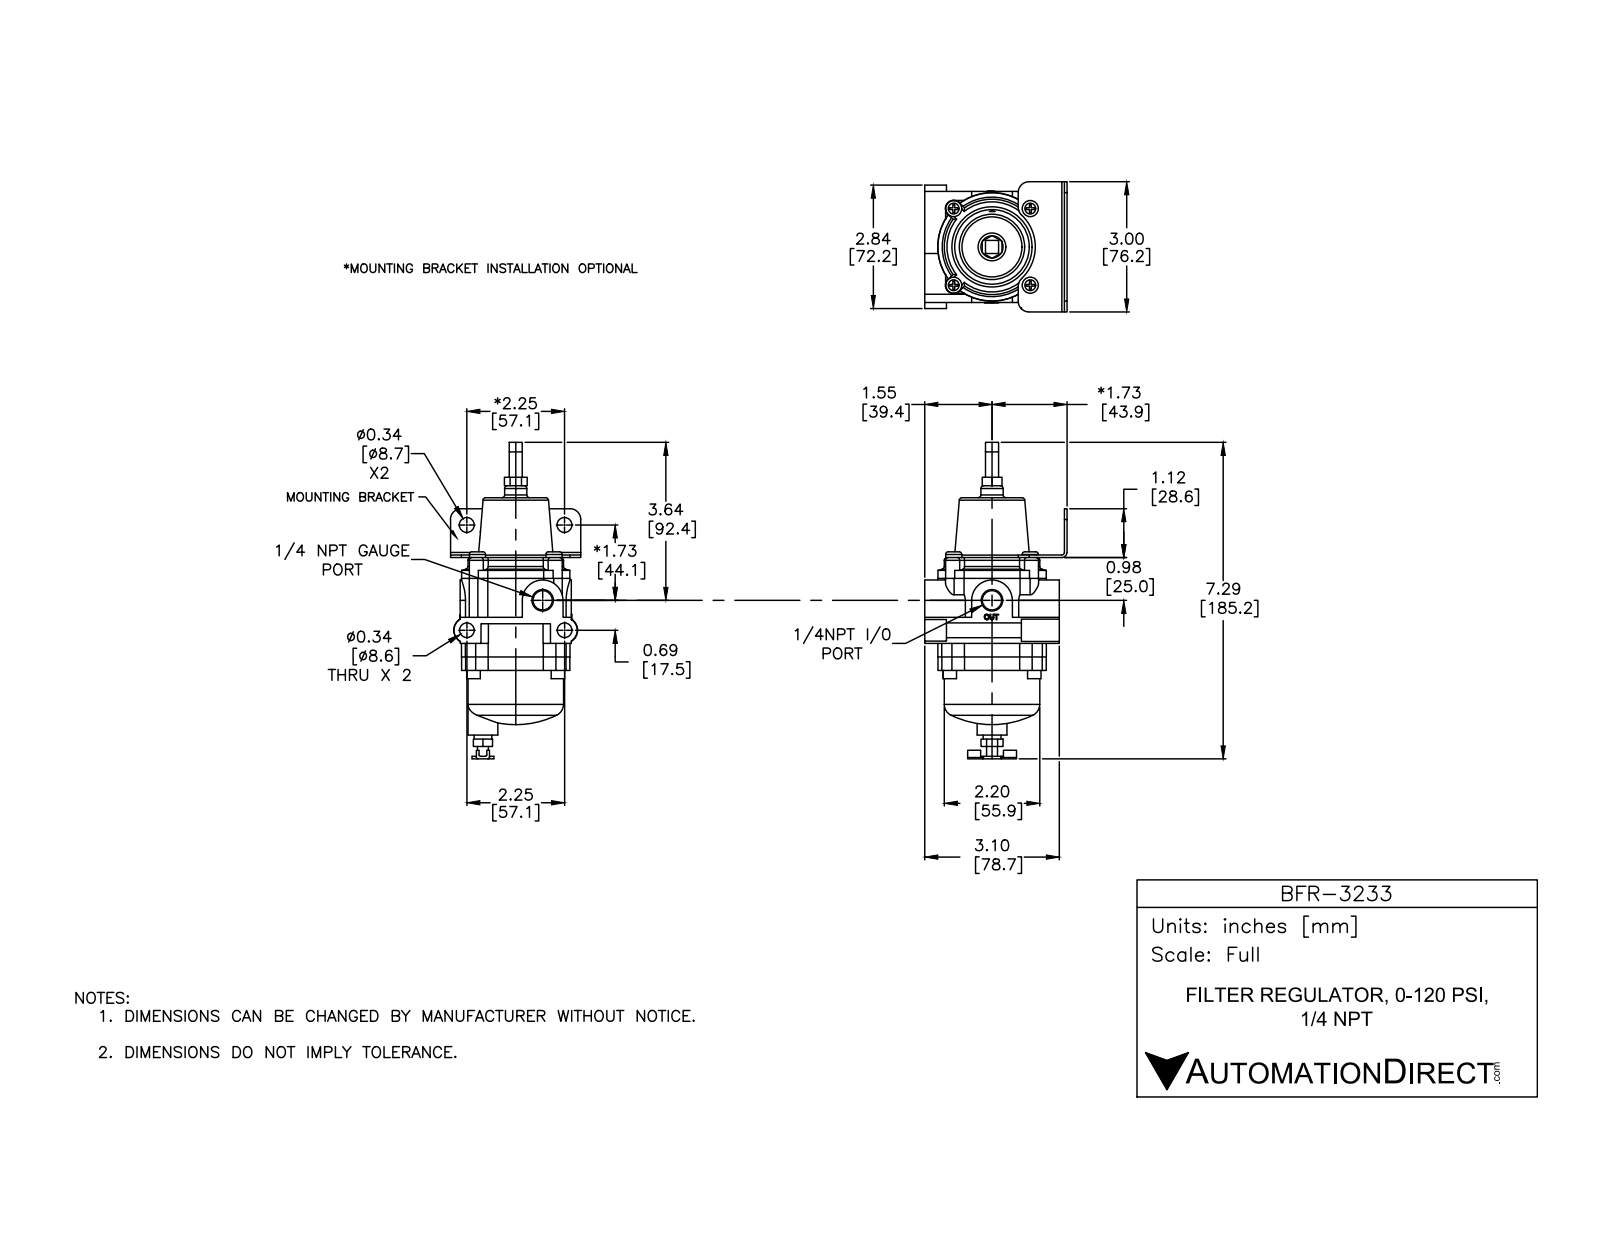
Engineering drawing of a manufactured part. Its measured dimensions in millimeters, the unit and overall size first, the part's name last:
Units: millimetres
Overall size (bounding box): 185.9 × 78.7 × 72.4
Round holes (diameter × count): ⌀4 ×8, ⌀5.1 ×8, ⌀8.6 ×2, ⌀11.1 ×2, ⌀3.2 ×1, ⌀6.5 ×1, ⌀6.6 ×1, ⌀8.4 ×1
Round bosses / shafts (diameter × count): ⌀4.8 ×8, ⌀3.8 ×8, ⌀7.9 ×5, ⌀9.5 ×4, ⌀55.9 ×1, ⌀17.5 ×1, ⌀13 ×1, ⌀10.6 ×1
Partial cylindrical surfaces — rounded edges, fillets, slot ends (radius × count): R0.1 ×48, R2.5 ×8, R4.7 ×8, R4.8 ×8, R0.5 ×6, R1.6 ×4, R1.6 ×3, R1 ×2
Main face-to-face distances: 46, 23.2, 22.7, 7.9, 31.1, 53.8, 15.2, 15.9, 8, 38
Hole centre spacings: 47.2, 3.2, 49.4, 34.9, 25.3, 31.8, 31.8, 44.9
Volume: 352 800 mm³ · Surface area: 68 320 mm²
Bodies: 15 solids, 1546 faces (316 planar, 994 cylindrical, 236 other)
Part name (STEP PRODUCT): BFR-3233
STEP written by: SolidWorks 2015 (CONFIG_CONTROL_DESIGN)
